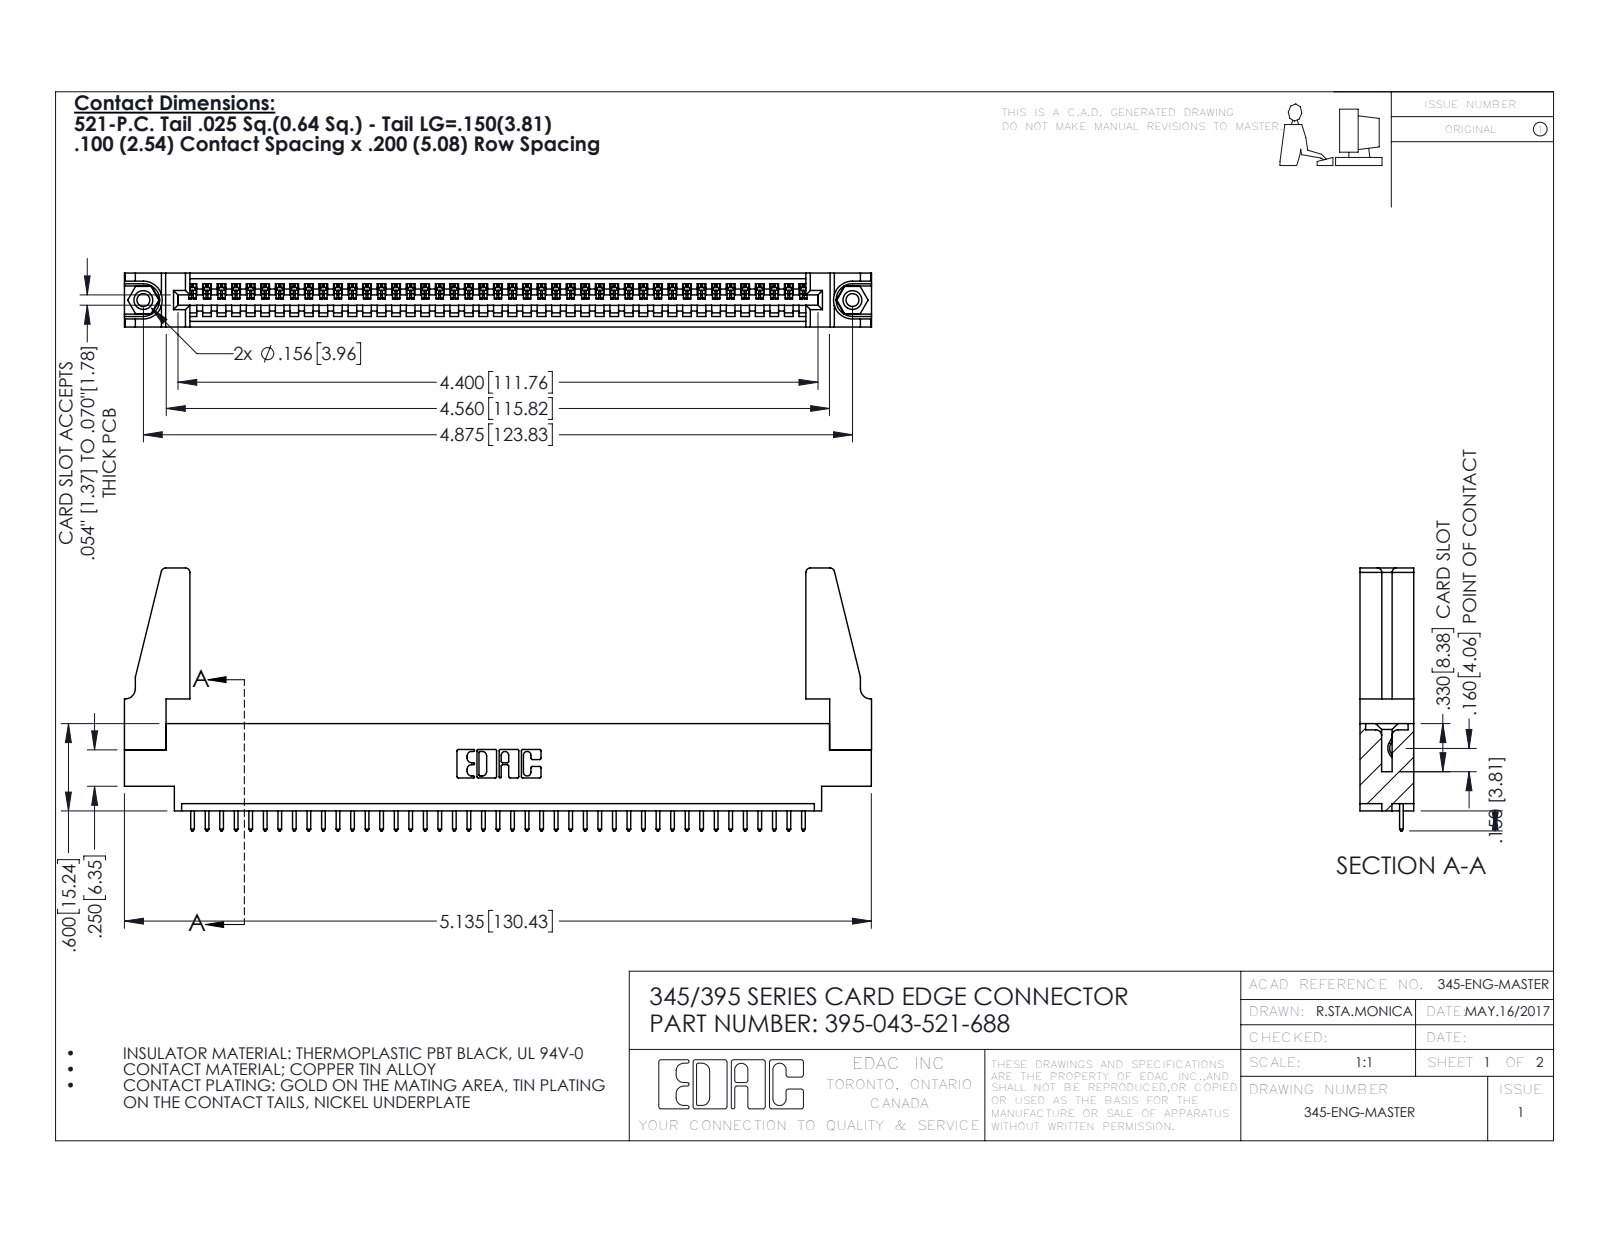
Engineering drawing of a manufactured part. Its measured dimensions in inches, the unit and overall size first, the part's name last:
Units: inches
Overall size (bounding box): 5.136 × 1.807 × 0.37
Round holes (diameter × count): ⌀0.089 ×2, ⌀0.125 ×2, ⌀0.156 ×2, ⌀0.064 ×1
Round bosses / shafts (diameter × count): ⌀0.155 ×2
Partial cylindrical surfaces — rounded edges, fillets, slot ends (radius × count): R0.006 ×86, R0.01 ×86, R0.01 ×22, R0.03 ×8, R0.007 ×6, R0.031 ×6, R0.026 ×3, R0.031 ×2
Main face-to-face distances: 0.072, 0.37, 0.298, 0.2, 0.098, 0.272, 0.025, 0.225, 0.175, 0.149
Hole centre spacings: 0.27, 4.639, 4.875
Volume: 0.941 in³ · Surface area: 29.38 in²
Bodies: 48 solids, 2748 faces (1876 planar, 856 cylindrical, 16 other)
Part name (STEP PRODUCT): 345-250-001_345-250-001-102; 395-043-521-688; 345-220-078_345-220-088; 345-292-001_345-293-121 (+1 more)
STEP written by: SolidWorks 2016 (CONFIG_CONTROL_DESIGN)
